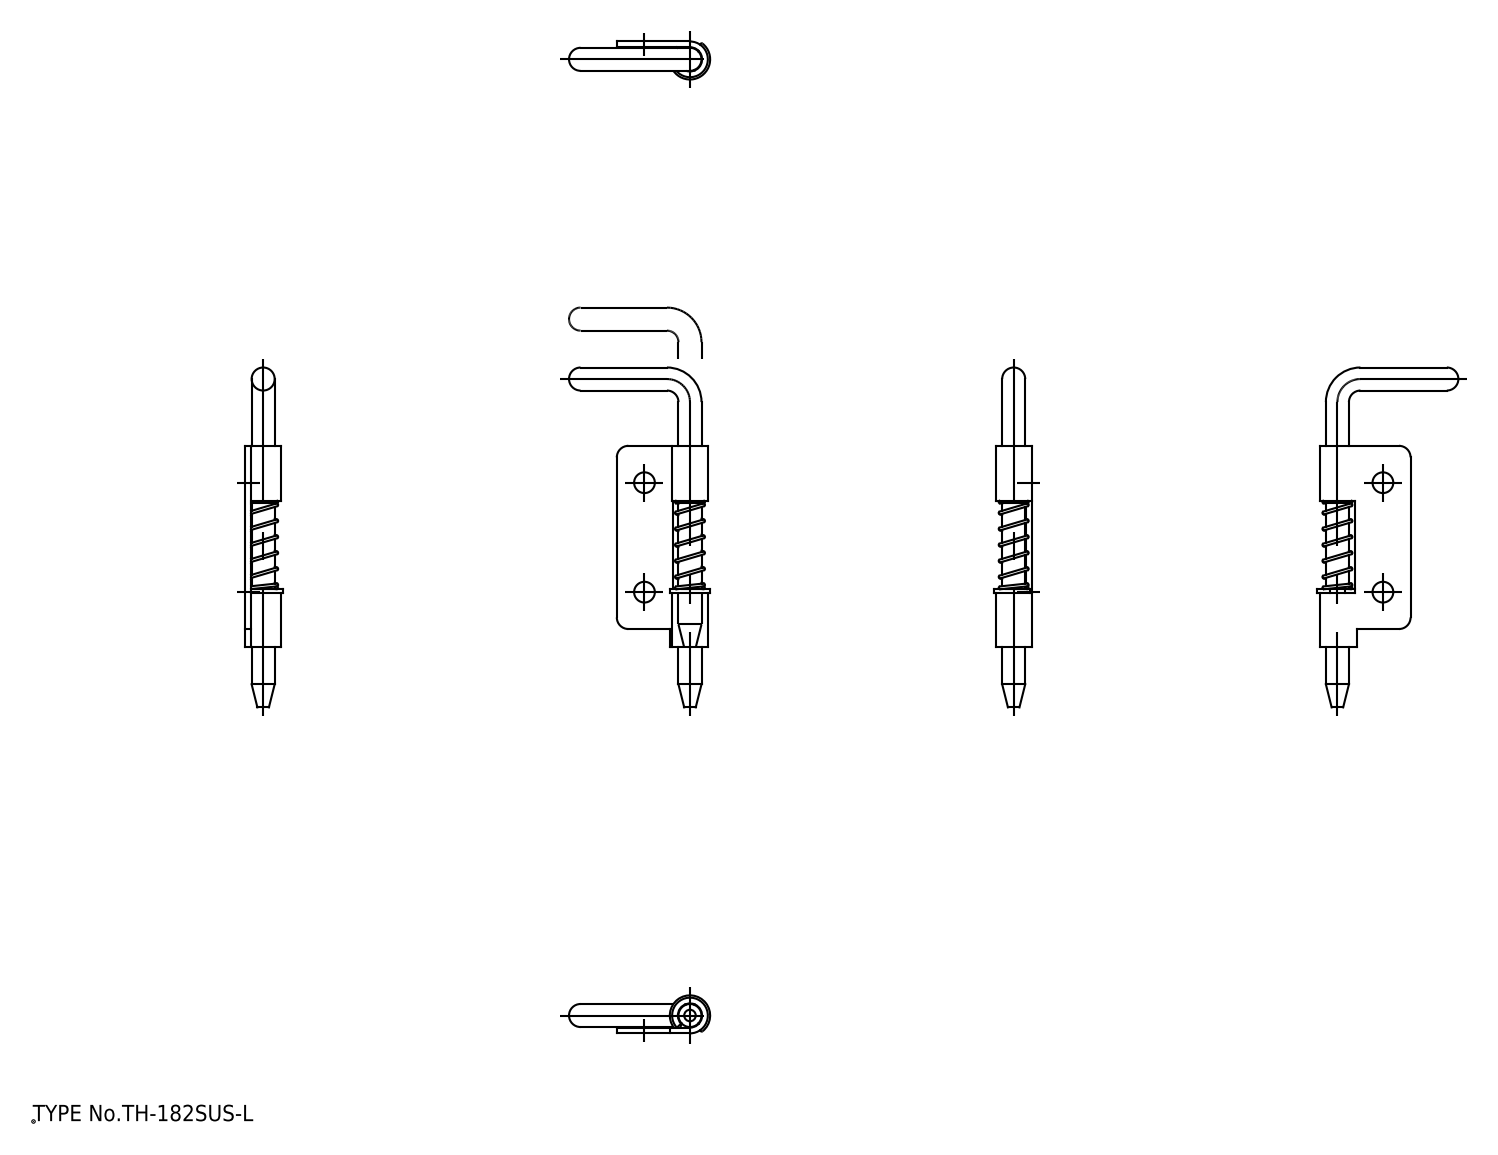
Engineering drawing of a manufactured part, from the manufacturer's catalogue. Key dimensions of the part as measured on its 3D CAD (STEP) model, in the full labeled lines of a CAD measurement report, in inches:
Part name (STEP PRODUCT): シャフト; ヒンジピース; スプリング_M2
STEP written by: spGate 18.9.1 (****-****-****-****) (AUTOMOTIVE_DESIGN)
Units: inches
Bodies: 3 solids, 88 faces (27 planar, 27 cylindrical, 34 other)
Overall size (bounding box): 2.323 × 0.965 × 0.26
Volume: 0.096 in³ · Surface area: 3.999 in²
Round holes (diameter × count): ⌀0.142 ×2, ⌀0.165 ×1
Round bosses / shafts (diameter × count): ⌀0.157 ×2, ⌀0.244 ×1, ⌀0.12 ×1
Partial cylindrical surfaces — rounded edges, fillets, slot ends (radius × count): R0.01 ×6, R0.079 ×2, R0.102 ×1, R0.138 ×1
Main face-to-face distances: 0.039, 1.004, 0.374, 0.024, 0.98, 0.398, 1.378, 0.63, 0.606, 0.382
Hole centre spacings: 0.748
